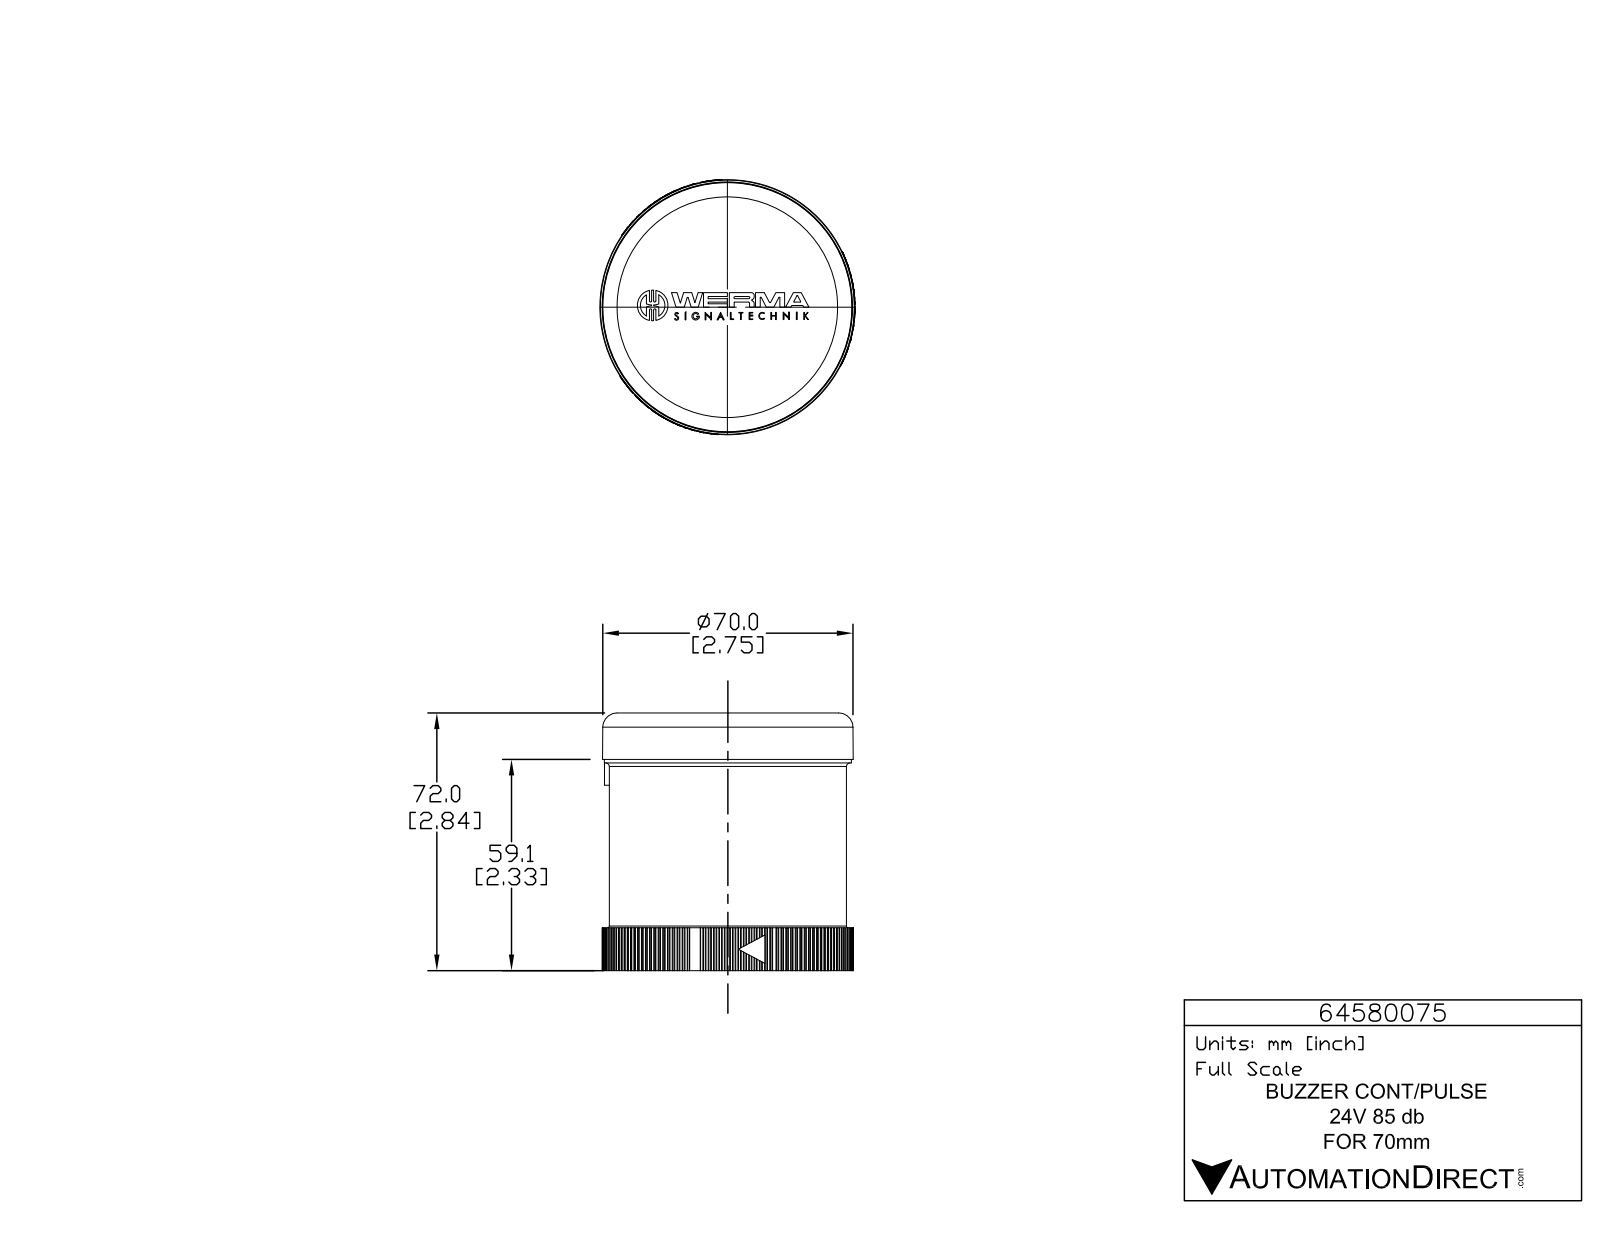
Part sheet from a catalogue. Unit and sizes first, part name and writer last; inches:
Units: inches
Overall size (bounding box): 2.762 × 2.762 × 2.705
Round holes (diameter × count): ⌀0.039 ×3, ⌀2.575 ×1
Round bosses / shafts (diameter × count): ⌀0.226 ×3, ⌀0.056 ×3, ⌀2.762 ×1, ⌀2.717 ×1, ⌀2.606 ×1
Partial cylindrical surfaces — rounded edges, fillets, slot ends (radius × count): R0.008 ×285, R0.008 ×6, R0.008 ×6, R0.008 ×6, R0.131 ×6, R0.004 ×3, R0.005 ×3, R0.008 ×3
Main face-to-face distances: 2.327, 2.451, 0.378, 2.705, 2.452, 0.472, 0.094, 2.232, 2.452, 2.452
Volume: 13.05 in³ · Surface area: 38.6 in²
Bodies: 1 solid, 1402 faces (832 planar, 563 cylindrical, 7 other)
Part name (STEP PRODUCT): 64580075
STEP written by: SolidWorks 2015 (AUTOMOTIVE_DESIGN)
